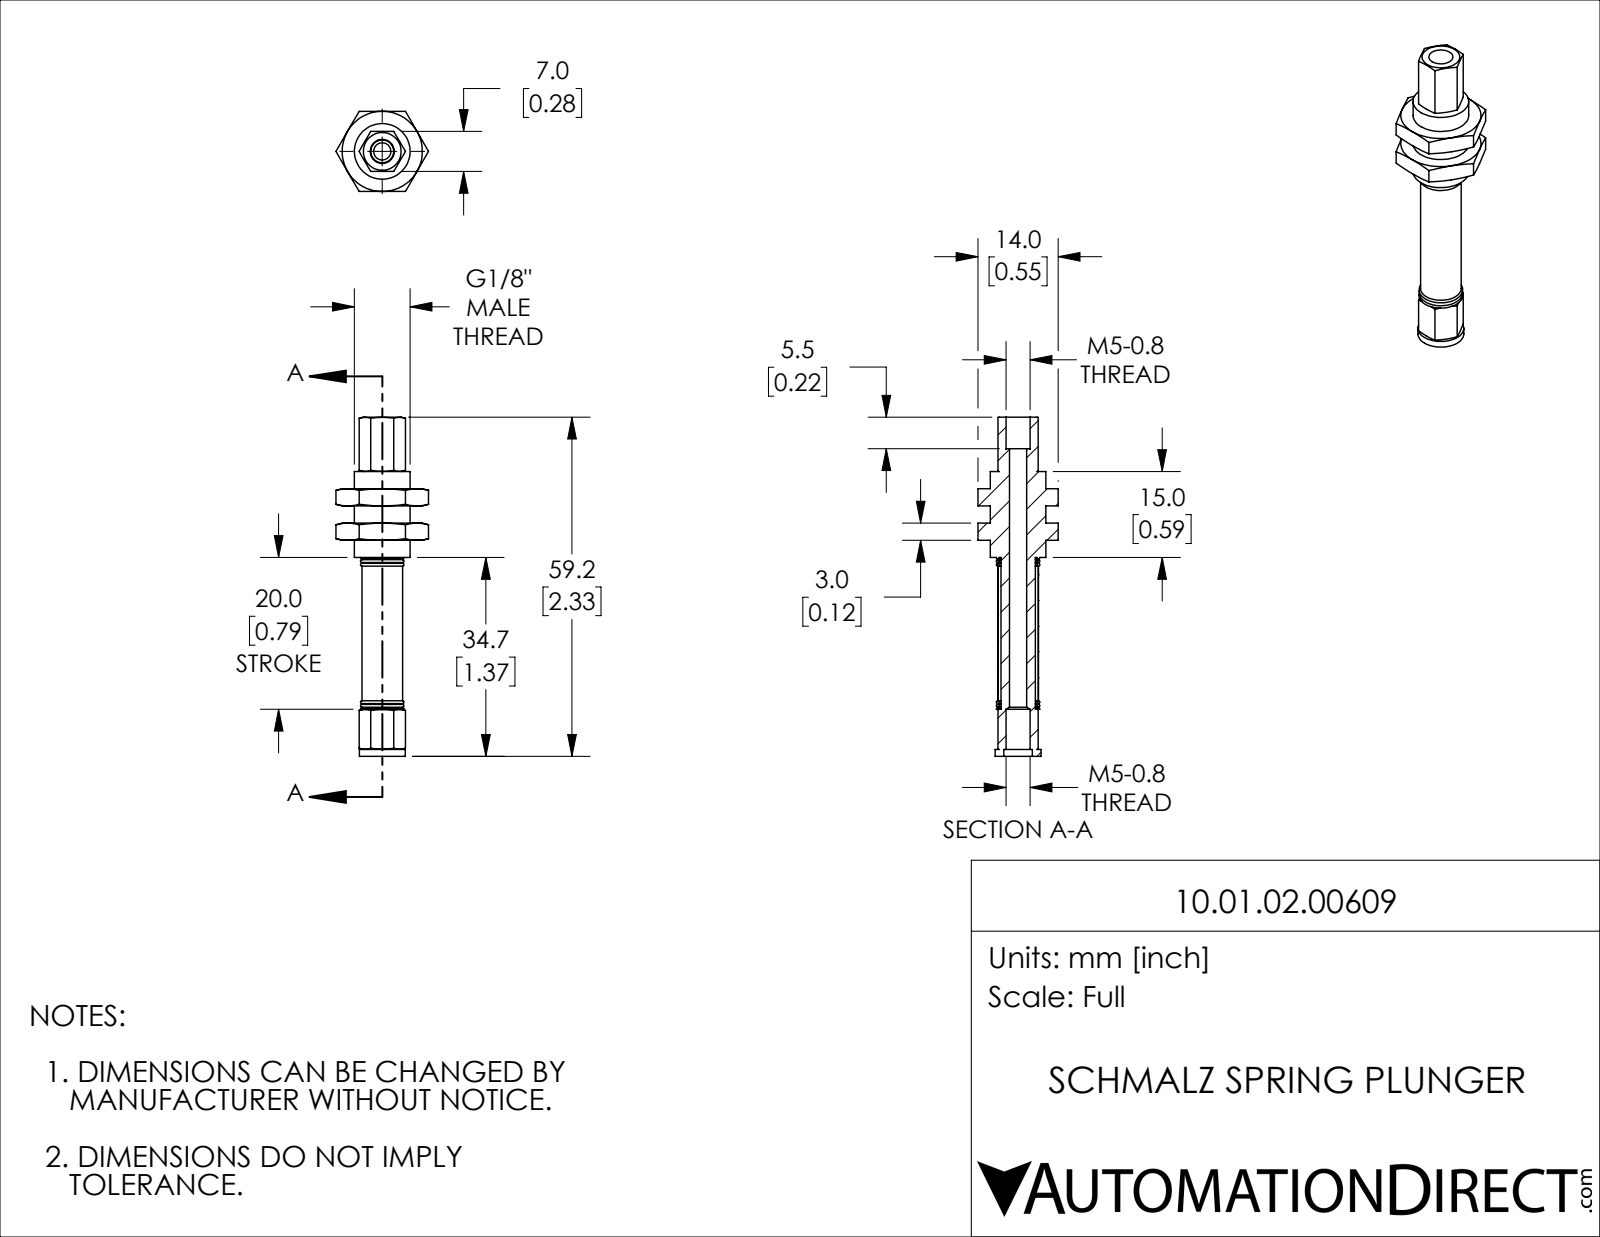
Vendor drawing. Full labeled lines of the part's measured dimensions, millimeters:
Part name (STEP PRODUCT): 10.01.02.00609
STEP written by: SolidWorks 2021 (CONFIG_CONTROL_DESIGN)
Units: millimetres
Bodies: 1 solid, 148 faces (38 planar, 38 cylindrical, 72 other)
Overall size (bounding box): 59.2 × 16.17 × 14
Volume: 2 693 mm³ · Surface area: 3 921 mm²
Round holes (diameter × count): ⌀3 ×1, ⌀4.2 ×1, ⌀5 ×1, ⌀7.1 ×1
Round bosses / shafts (diameter × count): ⌀9.73 ×1, ⌀8 ×1, ⌀7.1 ×1, ⌀6 ×1
Main face-to-face distances: 3, 3.5, 10.5, 6, 7, 9, 14, 12, 15, 34.7
